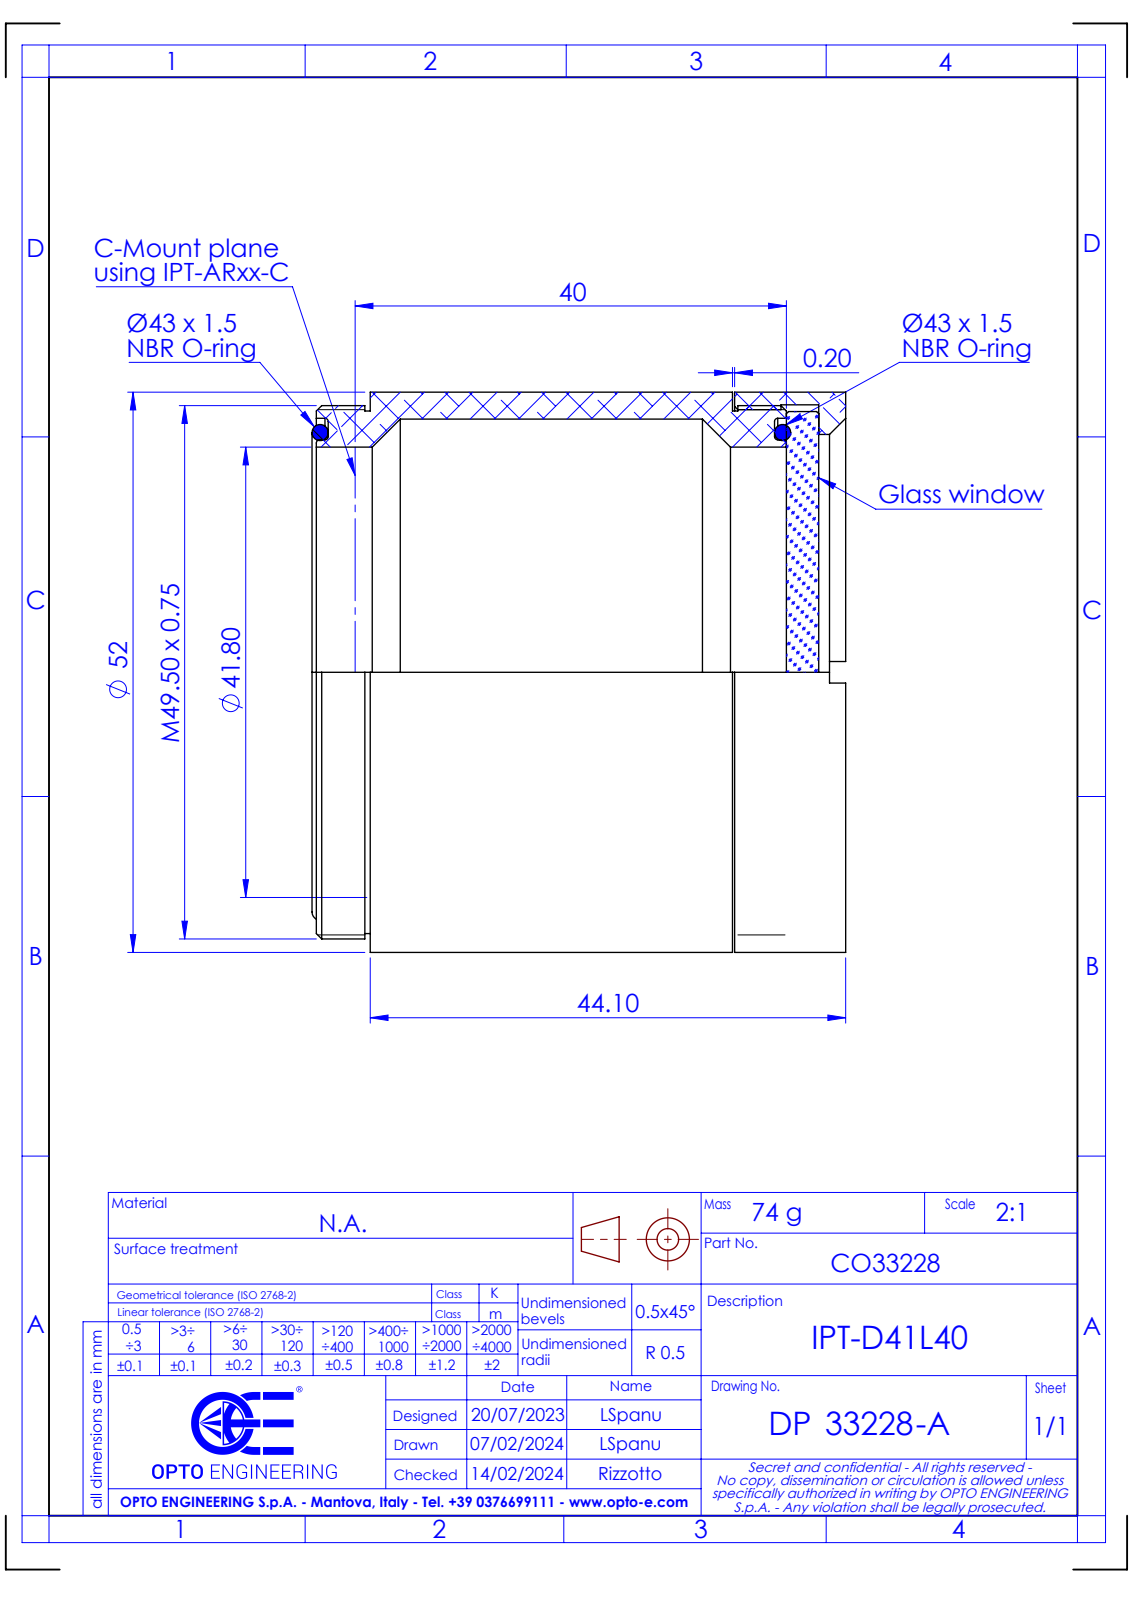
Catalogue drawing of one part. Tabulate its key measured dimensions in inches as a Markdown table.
| quantity | value |
| --- | --- |
| part name | DP33228-A_IPT-D41L40 |
| STEP written by | SolidWorks 2021 (CONFIG_CONTROL_DESIGN) |
| units | inches |
| bodies | 0 solids, 45 faces (15 planar, 16 cylindrical, 14 other) |
| overall size | 2.047 × 2.047 × 1.949 |
| round holes (diameter × count) | 1.646 × 1, 1.738 × 1, 1.85 × 1, 1.856 × 1 |
| round bosses / shafts (diameter × count) | 2.047 × 1, 1.949 × 1, 1.909 × 1 |
| main face-to-face distances | 0.098, 0.315, 0.413, 1.323, 1.638, 1.736, 1.331, 0.307, 0.406, 0.154 |
